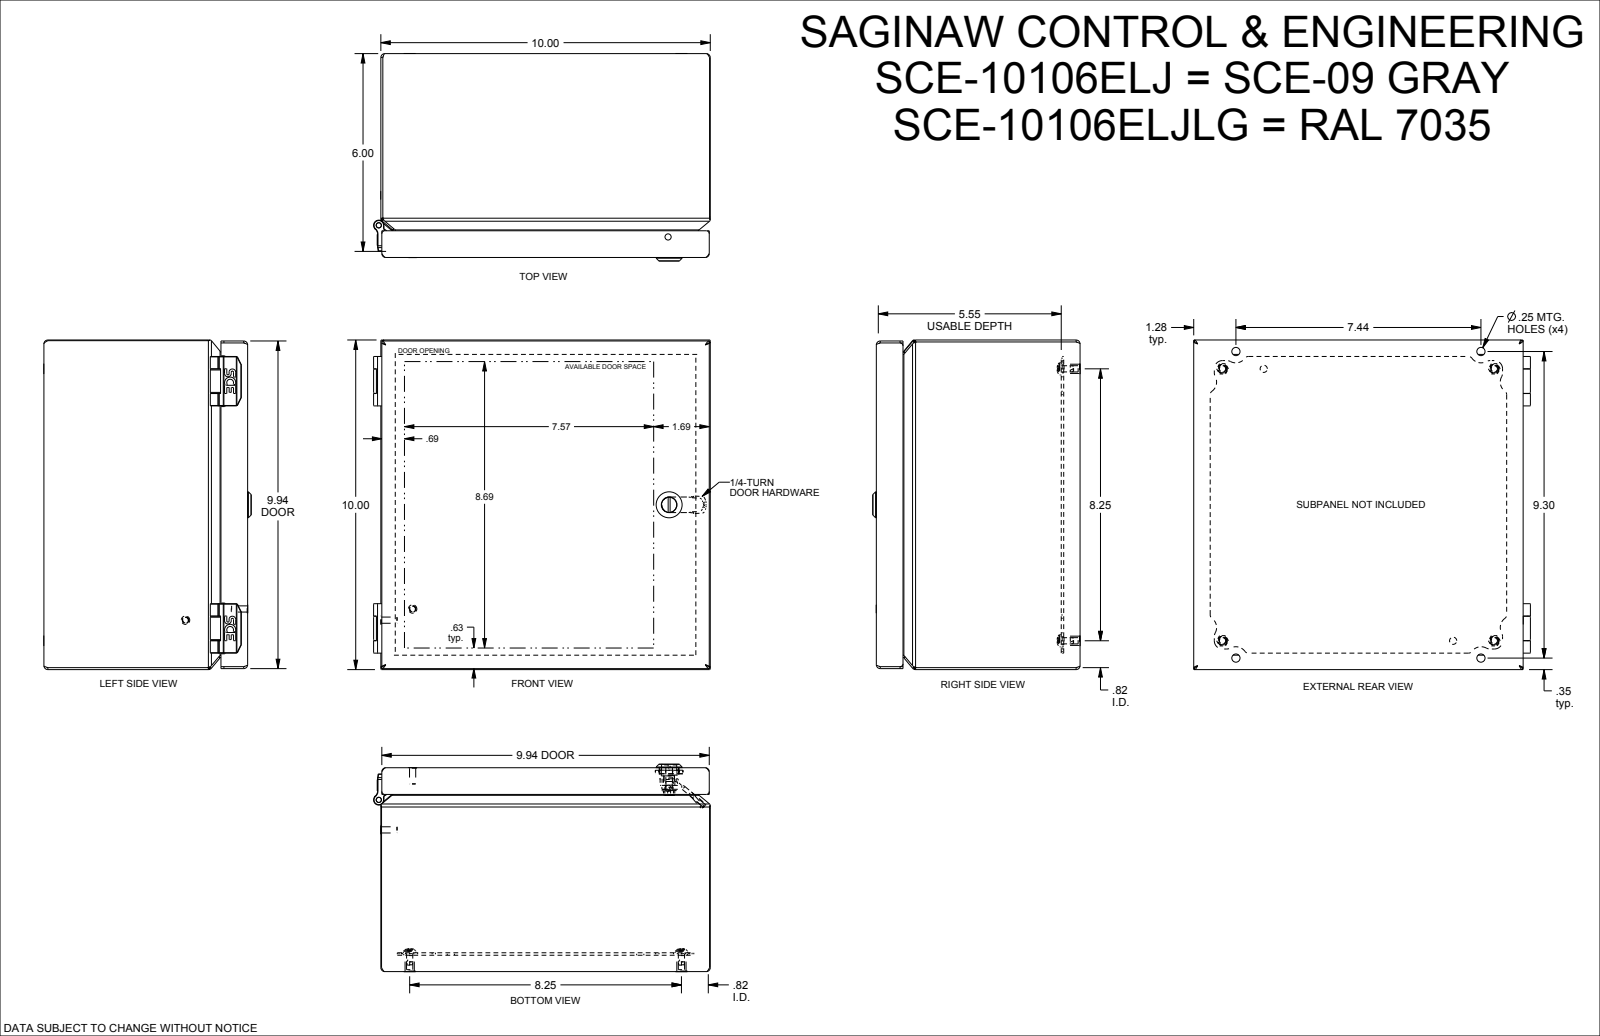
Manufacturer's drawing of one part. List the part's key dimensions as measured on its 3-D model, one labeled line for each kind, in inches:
Part name (STEP PRODUCT): SCE-10106ELJ
STEP written by: SolidWorks 2019 (AUTOMOTIVE_DESIGN)
Units: inches
Bodies: 34 solids, 1083 faces (394 planar, 353 cylindrical, 336 other)
Overall size (bounding box): 10.22 × 10.06 × 6.296
Volume: 37.38 in³ · Surface area: 1 175 in²
Round holes (diameter × count): ⌀0.25 ×8, ⌀0.17 ×4, ⌀0.19 ×4, ⌀0.284 ×4, ⌀0.02 ×2, ⌀0.1 ×2, ⌀0.218 ×2, ⌀0.266 ×2, ⌀0.158 ×1, ⌀0.196 ×1, ⌀0.2 ×1, ⌀0.239 ×1
Round bosses / shafts (diameter × count): ⌀0.188 ×6, ⌀0.479 ×4, ⌀0.373 ×4, ⌀0.28 ×4, ⌀0.16 ×4, ⌀0.26 ×2, ⌀0.256 ×2, ⌀0.237 ×2
Partial cylindrical surfaces — rounded edges, fillets, slot ends (radius × count): R0.03 ×28, R0.025 ×24, R0.013 ×21, R0.05 ×16, R0.25 ×13, R0.125 ×11, R0.01 ×10, R0.06 ×10
Main face-to-face distances: 0.059, 10.001, 0.06, 10.06, 9.942, 6.185, 6.126, 6.066, 6.125, 0.437
Hole centre spacings: 8.25, 8.31, 7.5, 0.06, 1.25, 4.142, 7, 7.438
